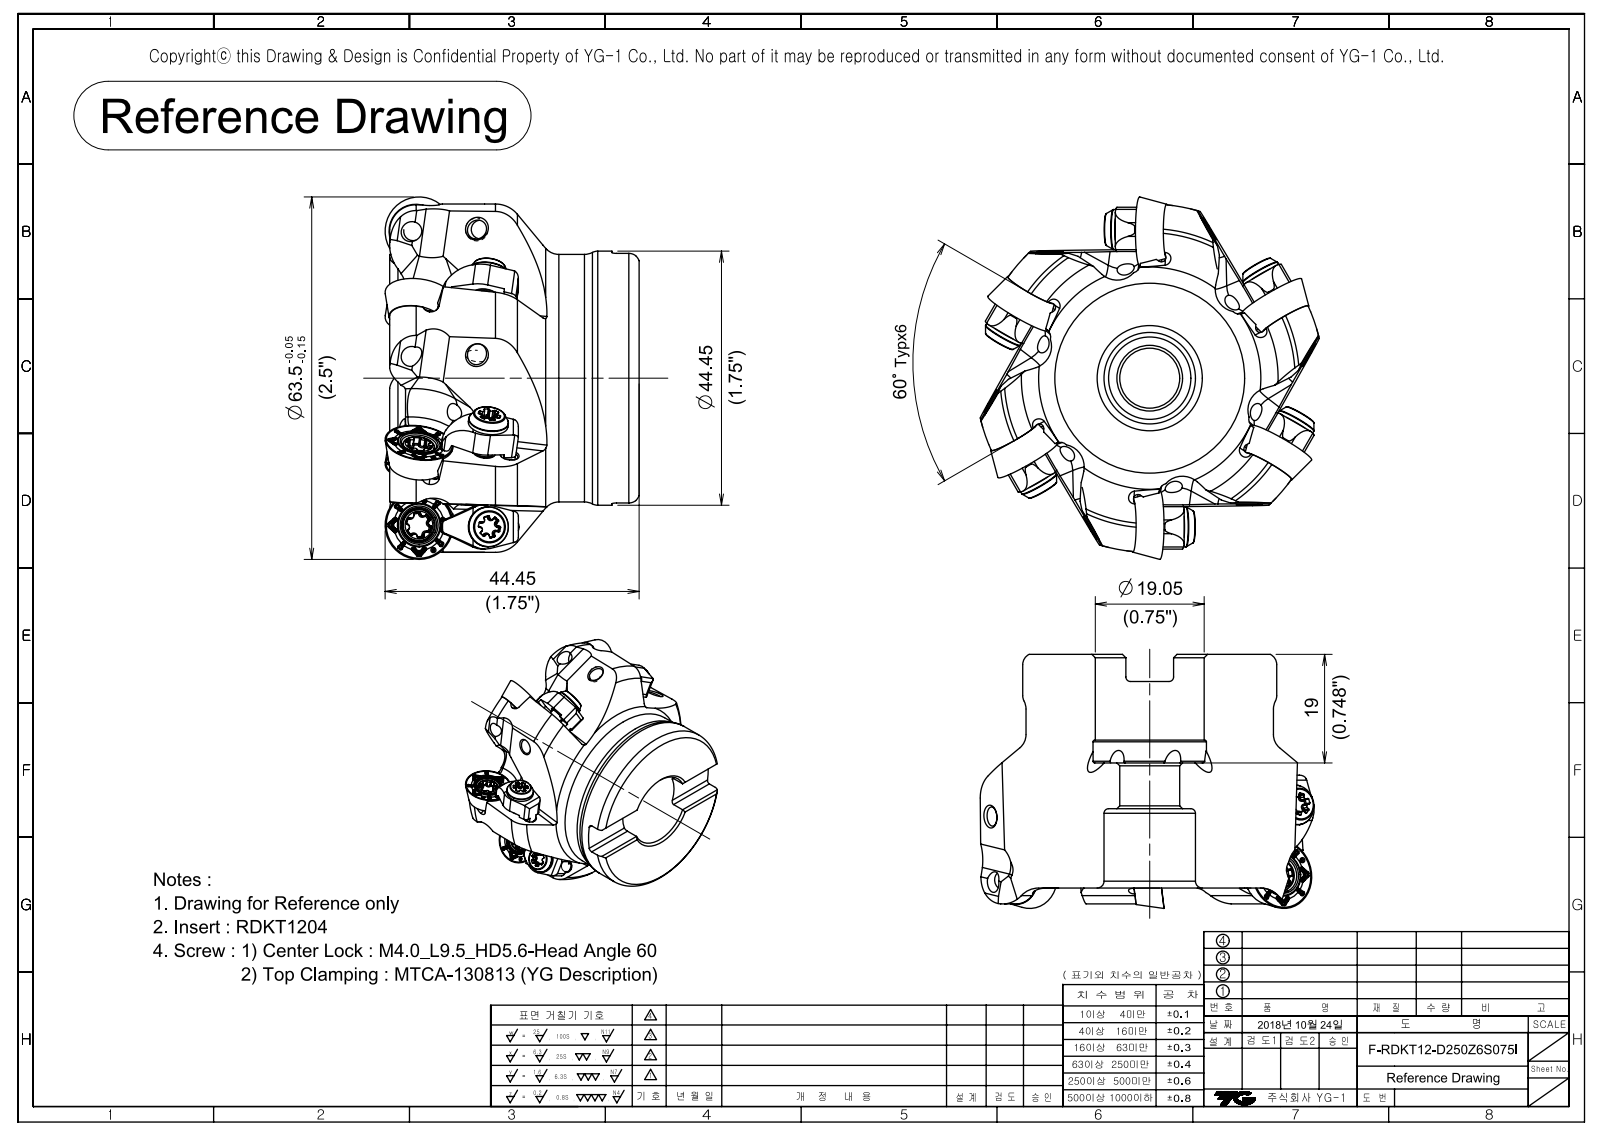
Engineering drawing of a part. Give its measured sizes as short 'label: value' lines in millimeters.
name: TURNING_F-RDKT12-D250Z6S075I
written by: SIEMENS PLM Software NX 10.0 (CONFIG_CONTROL_DESIGN)
unit: mm
bodies: 1 solid, 46 faces (18 planar, 11 cylindrical, 17 other)
size: 60.94 × 60.94 × 43.65
volume: 84 534 mm³; area: 13 985 mm²
holes: 1× ⌀10.49, 1× ⌀16, 1× ⌀19.05, 1× ⌀19.85
bosses: 1× ⌀60.93, 1× ⌀44.45, 1× ⌀43.3
rounds: 2× R0.8
face distances: 40.88, 21.88, 19, 36.13, 14.25, 4.75, 2.77, 24.65, 38.9, 43.65
